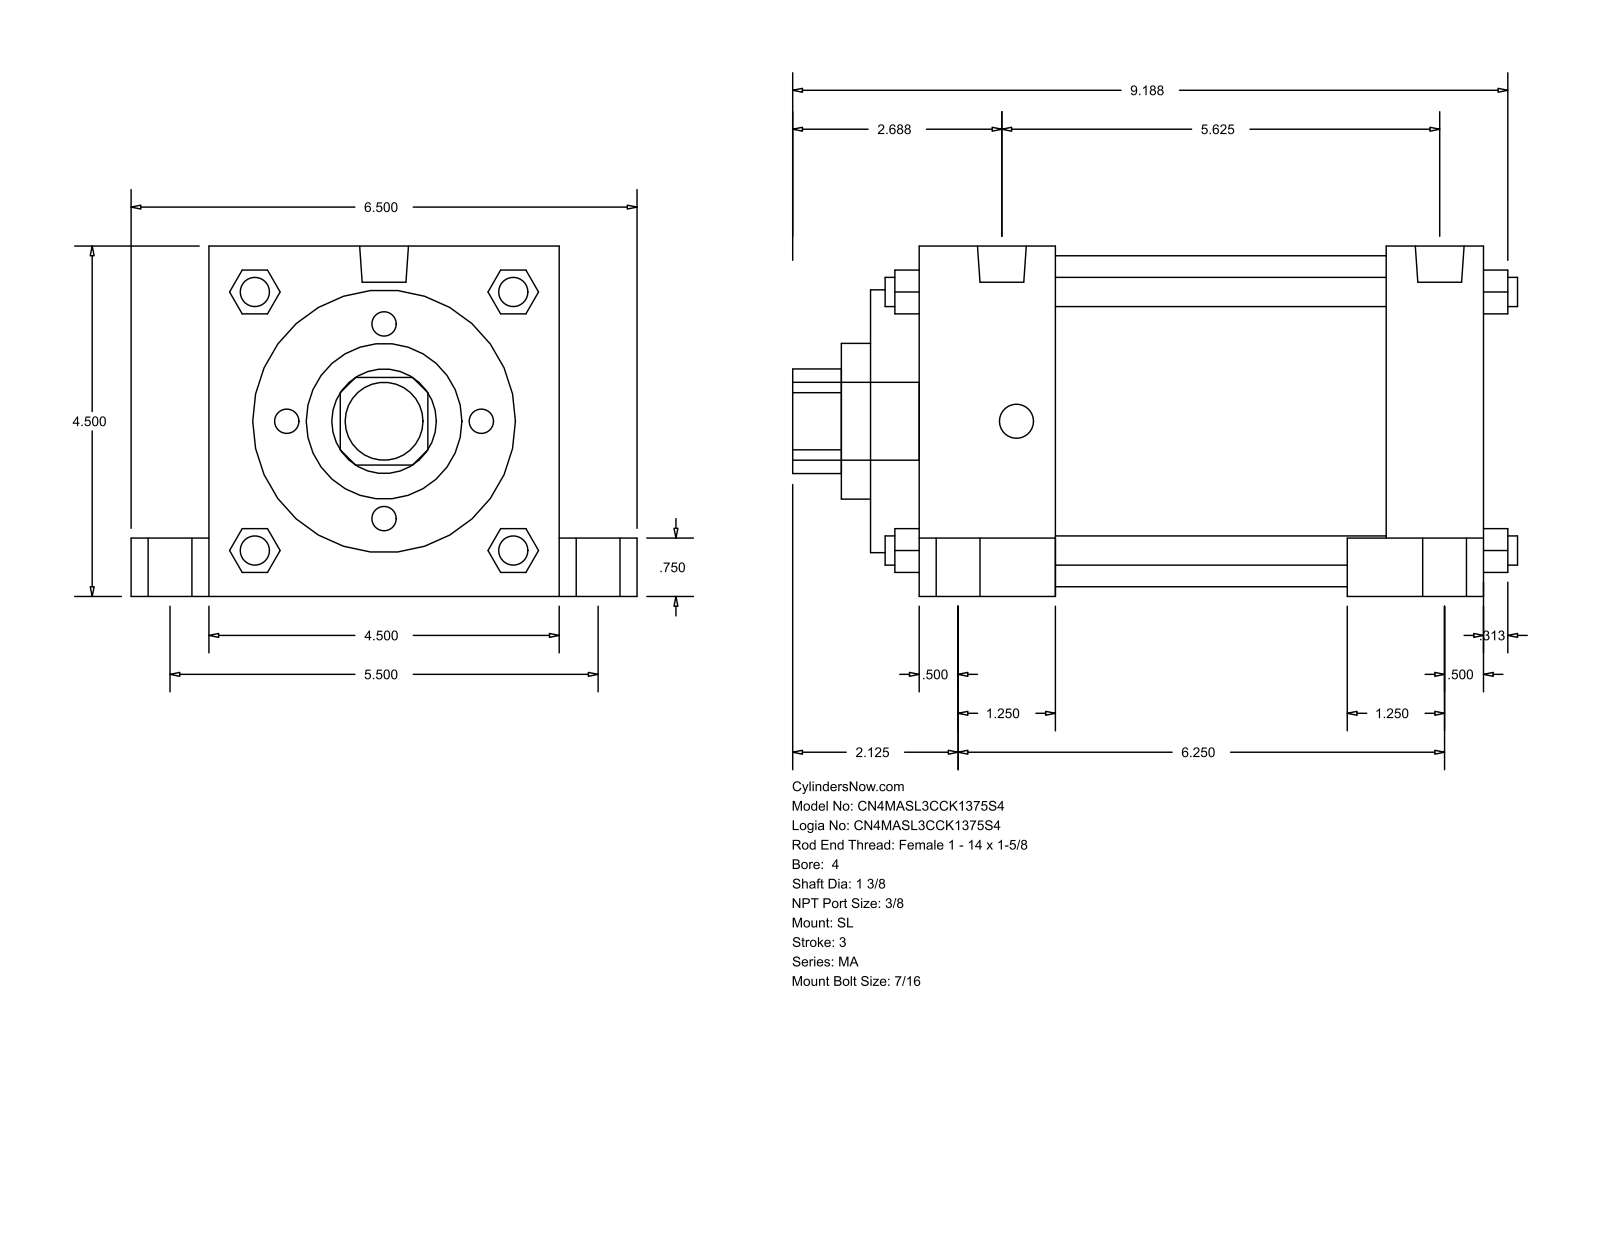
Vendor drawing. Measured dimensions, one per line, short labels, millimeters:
name: MA_SL__0400_1.375
written by: GSSL Pune (CONFIG_CONTROL_DESIGN)
unit: mm
bodies: 0 solids, 150 faces (113 planar, 37 cylindrical, 0 other)
size: 236.54 × 165.1 × 114.3
holes: 1× ⌀34.92, 1× ⌀50.8, 1× ⌀85.72, 1× ⌀107.95
bosses: 4× ⌀20.64, 4× ⌀14.29, 4× ⌀11.11, 4× ⌀9.53, 2× ⌀15.93, 1× ⌀25.4
rounds: 1× R17.06
face distances: 114.3, 184.16, 15.87, 200.03, 60.32, 44.45, 139.71, 168.28, 152.41, 107.96
